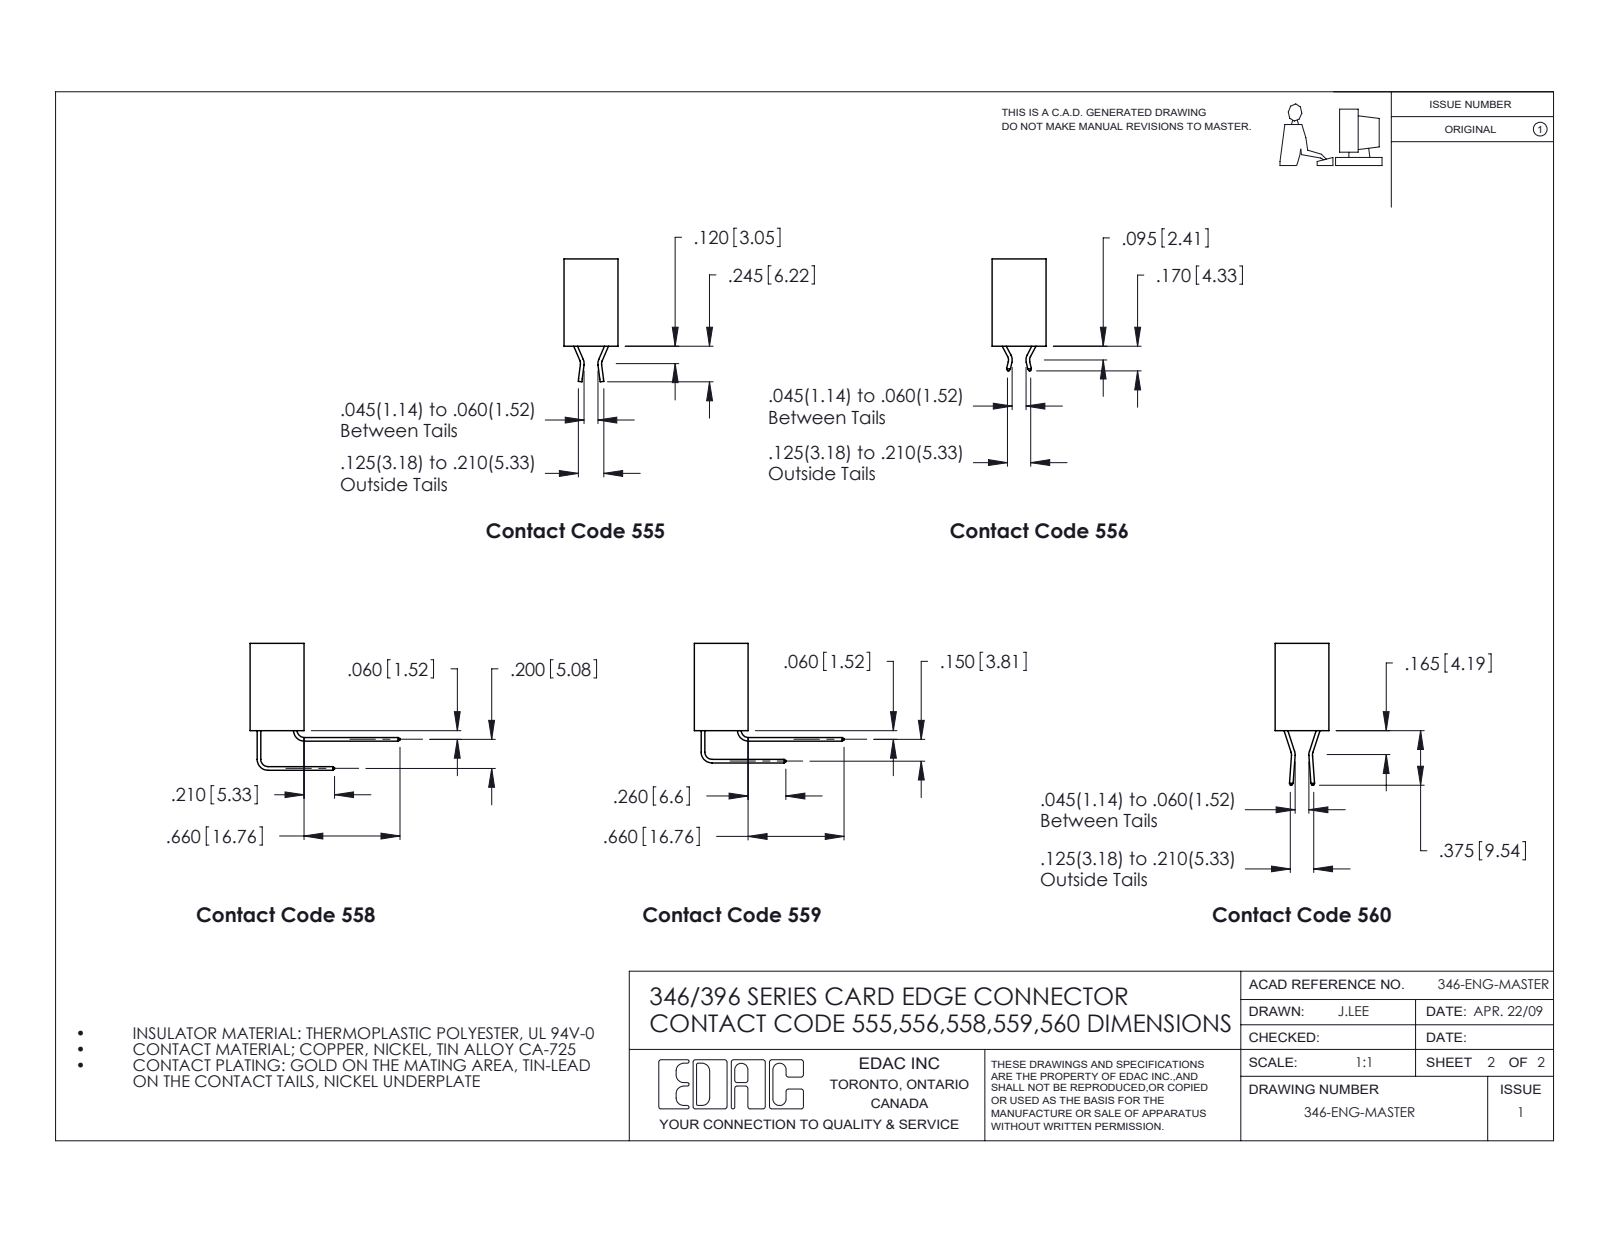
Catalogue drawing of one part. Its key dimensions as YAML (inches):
part_name: "345-292-001_555 Tail; 345-250-001_345-250-003-102; 346 Part_Flush Mounting Lugs - 0.156 Dia-TI; 346-074-555-208"
step_written_by: "SolidWorks 2020 (CONFIG_CONTROL_DESIGN)"
units: inches
bodies: {solids: 77, faces: 4474, planar: 2550, cylindrical: 1908, other: 16}
overall_size: [5.435, 0.845, 0.37]
volume: 0.832
surface_area: 30.14
round_holes:
  - {diameter: 0.089, count: 2}
  - {diameter: 0.125, count: 2}
  - {diameter: 0.156, count: 2}
  - {diameter: 0.064, count: 1}
round_bosses_or_shafts:
  - {diameter: 0.155, count: 2}
partial_cylinders:
  - {radius: 0.016, count: 148}
  - {radius: 0.02, count: 148}
  - {radius: 0.006, count: 111}
  - {radius: 0.01, count: 22}
  - {radius: 0.007, count: 6}
  - {radius: 0.031, count: 6}
  - {radius: 0.026, count: 3}
  - {radius: 0.01, count: 2}
face_to_face_distances: [0.048, 0.322, 0.37, 0.25, 0.025, 0.072, 0.298, 0.275, 0.148, 0.222]
hole_center_spacings: [0.246, 4.961, 5.17]
